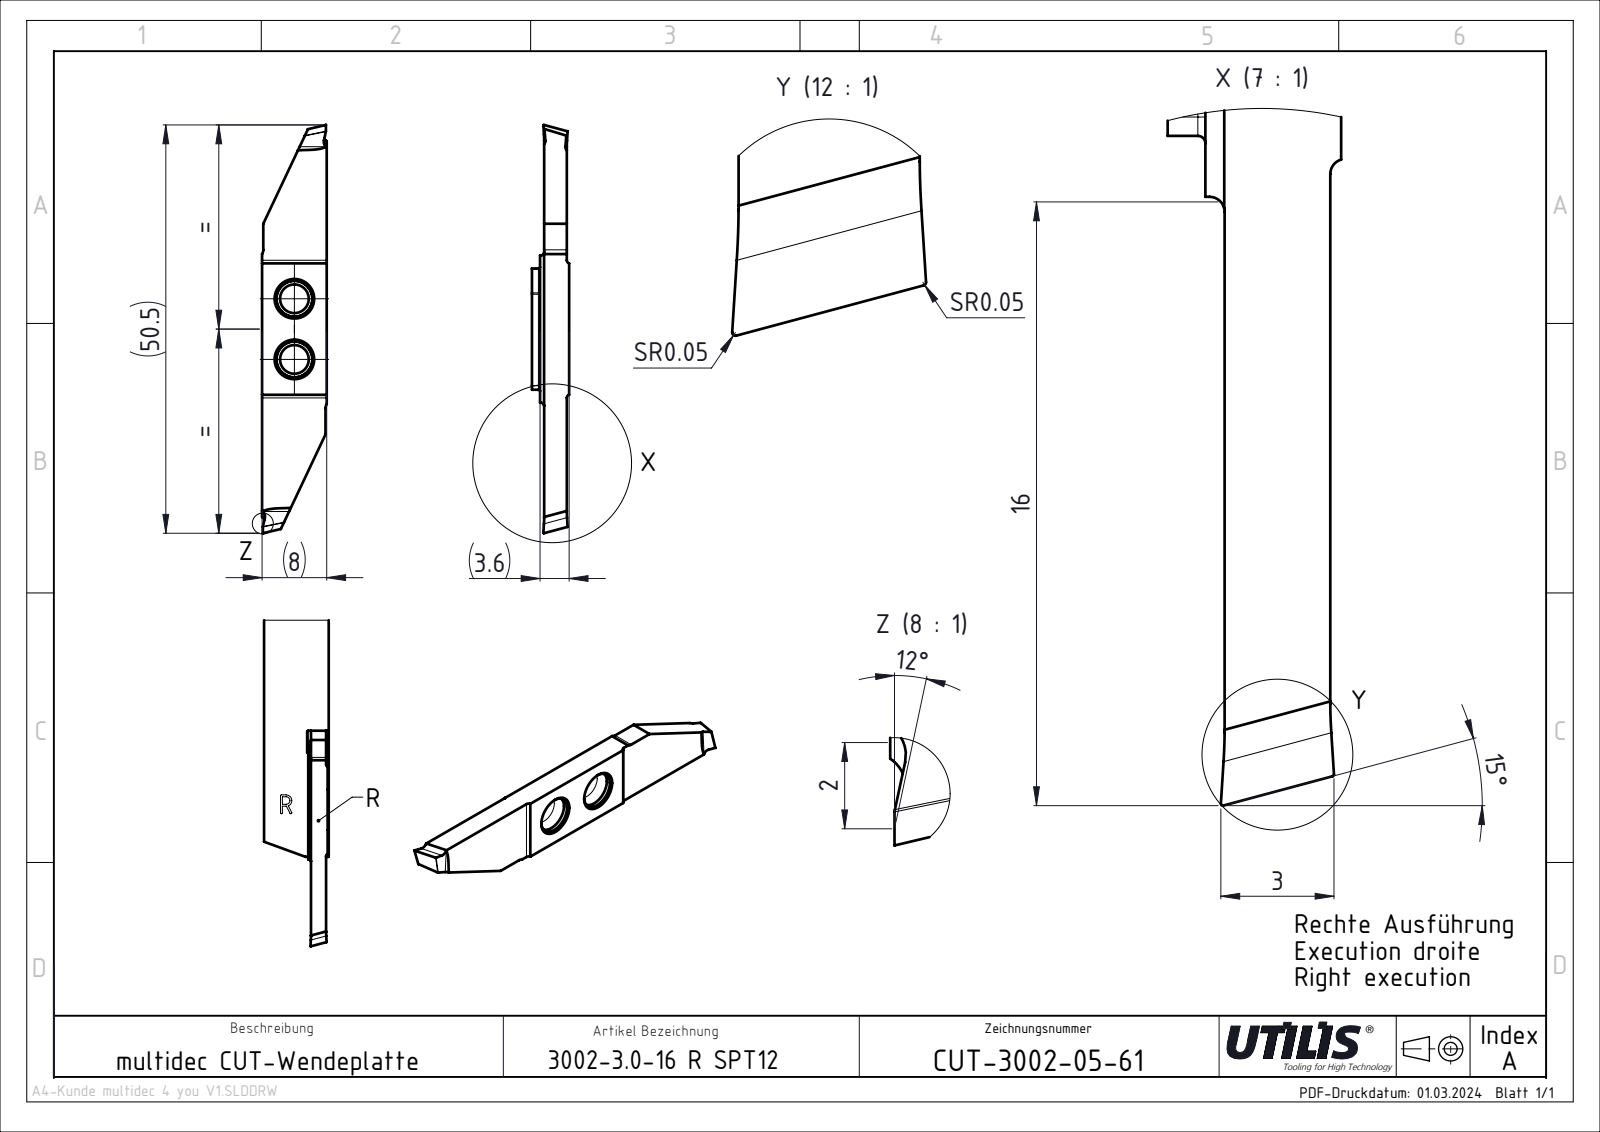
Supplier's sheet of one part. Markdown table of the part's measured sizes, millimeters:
| quantity | value |
| --- | --- |
| part name | CUT-3002 SPT Slim_and_Deep; ASME Y14.5 |
| STEP written by | SolidWorks 2023 SP4 \|\| FormatWorks Professional (AP242_MANAGED_MODEL_BASED_3D_ENGINEERING_MIM_LF) |
| units | millimeters |
| bodies | 1 solid, 36 faces (22 planar, 14 cylindrical, 0 other) |
| overall size | 50.5 × 8 × 3.6 |
| volume | 954 mm³ |
| surface area | 1 019 mm² |
| round holes (diameter × count) | 3.55 × 2 |
| partial cylindrical surfaces (radius × count) | 0.4 × 4, 1 × 2 |
| main face-to-face distances | 2.8, 3.09, 0.51, 3.31, 3.6, 8, 18.09, 7.85, 7.7, 0.41 |
| hole center spacings | 7.5 |
